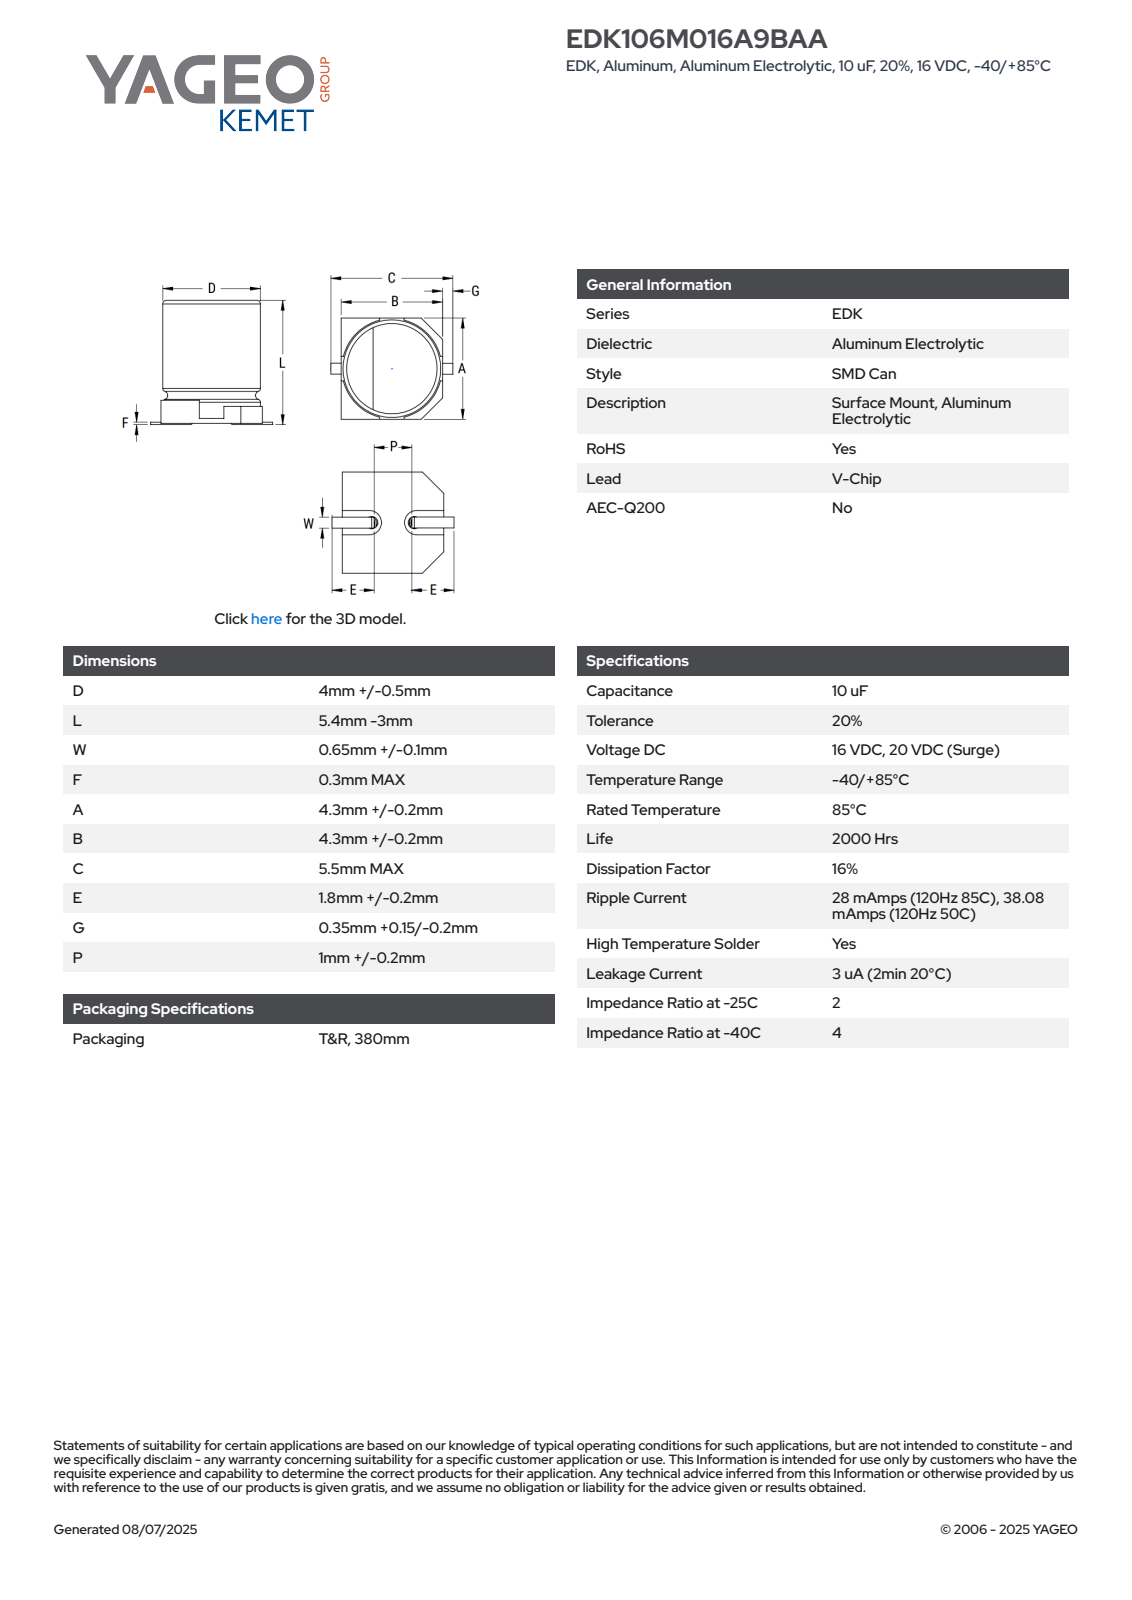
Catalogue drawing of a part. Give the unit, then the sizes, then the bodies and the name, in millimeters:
Units: millimetres
Overall size (bounding box): 5.2 × 4.5 × 2.4
Round bosses / shafts (diameter × count): ⌀4.3 ×1
Partial cylindrical surfaces — rounded edges, fillets, slot ends (radius × count): R0.2 ×2, R1.79 ×1, R2.25 ×1
Main face-to-face distances: 2.1, 1.98, 0.42, 2.4, 1.5, 0.6, 0.9, 0.48, 0.75, 4.5
Volume: 33 mm³ · Surface area: 108 mm²
Bodies: 5 solids, 78 faces (61 planar, 11 cylindrical, 6 other)
Part name (STEP PRODUCT): CAC_S_4X5.4_D4.5L5.65W0.75F0.3A4.5B4.5C5.5E2P1.2
STEP written by: SolidWorks 2021 (AUTOMOTIVE_DESIGN)
